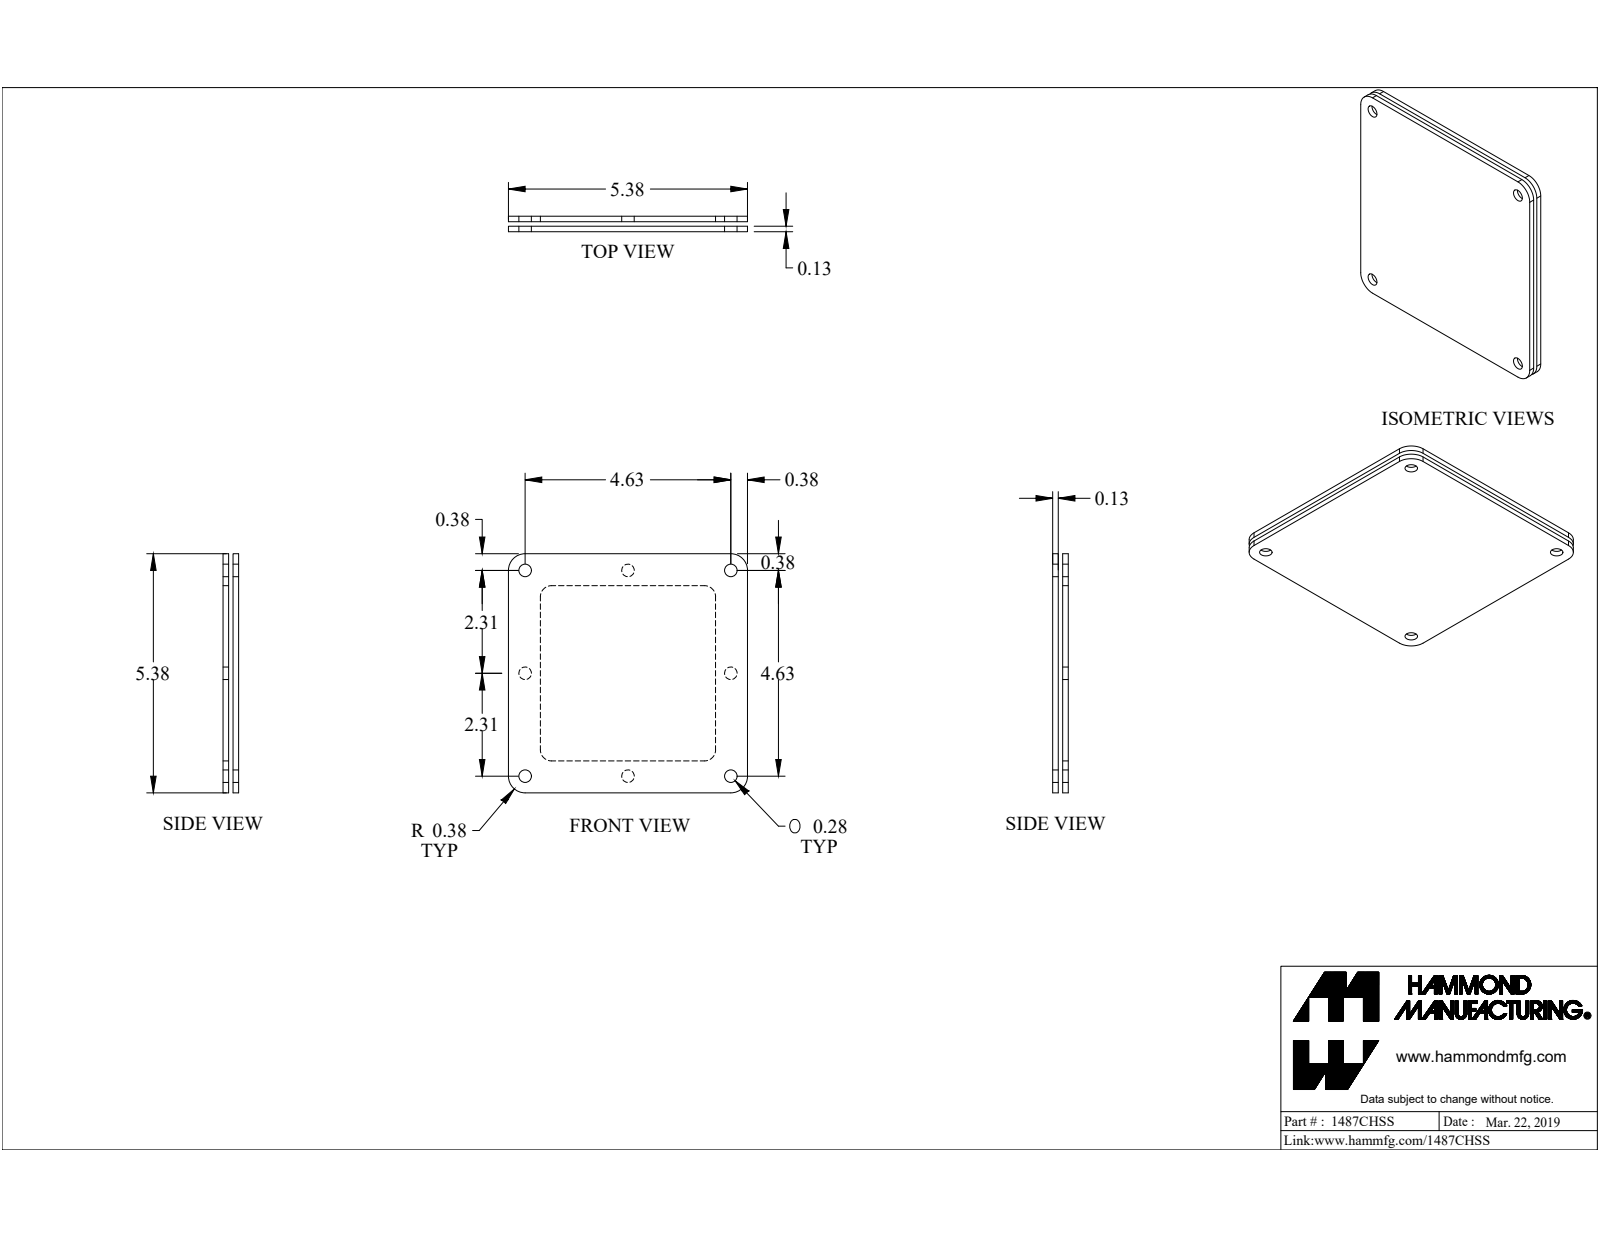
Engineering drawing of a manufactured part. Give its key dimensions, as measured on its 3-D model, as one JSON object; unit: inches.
{"part_name": "1487CHSS", "step_written_by": "SolidWorks 2019 (CONFIG_CONTROL_DESIGN)", "units": "inches", "bodies": {"solids": 5, "faces": 127, "planar": 73, "cylindrical": 46, "other": 8}, "overall_size": [5.375, 5.375, 0.971], "volume_in3": 5.257, "surface_area_in2": 93.41, "round_holes": [[0.281, 8], [0.196, 1], [0.258, 1], [0.35, 1]], "round_bosses_or_shafts": [[0.5, 1], [0.25, 1]], "partial_cylinders_radius": [[0.02, 6], [0.25, 4], [0.375, 4]], "face_to_face_distances": [0.125, 0.35, 0.225, 0.225, 0.1, 0.125, 5.375, 0.718, 4.657, 3.939], "hole_center_spacings": [2.313, 5.171, 4.625, 3.27, 6.541]}
